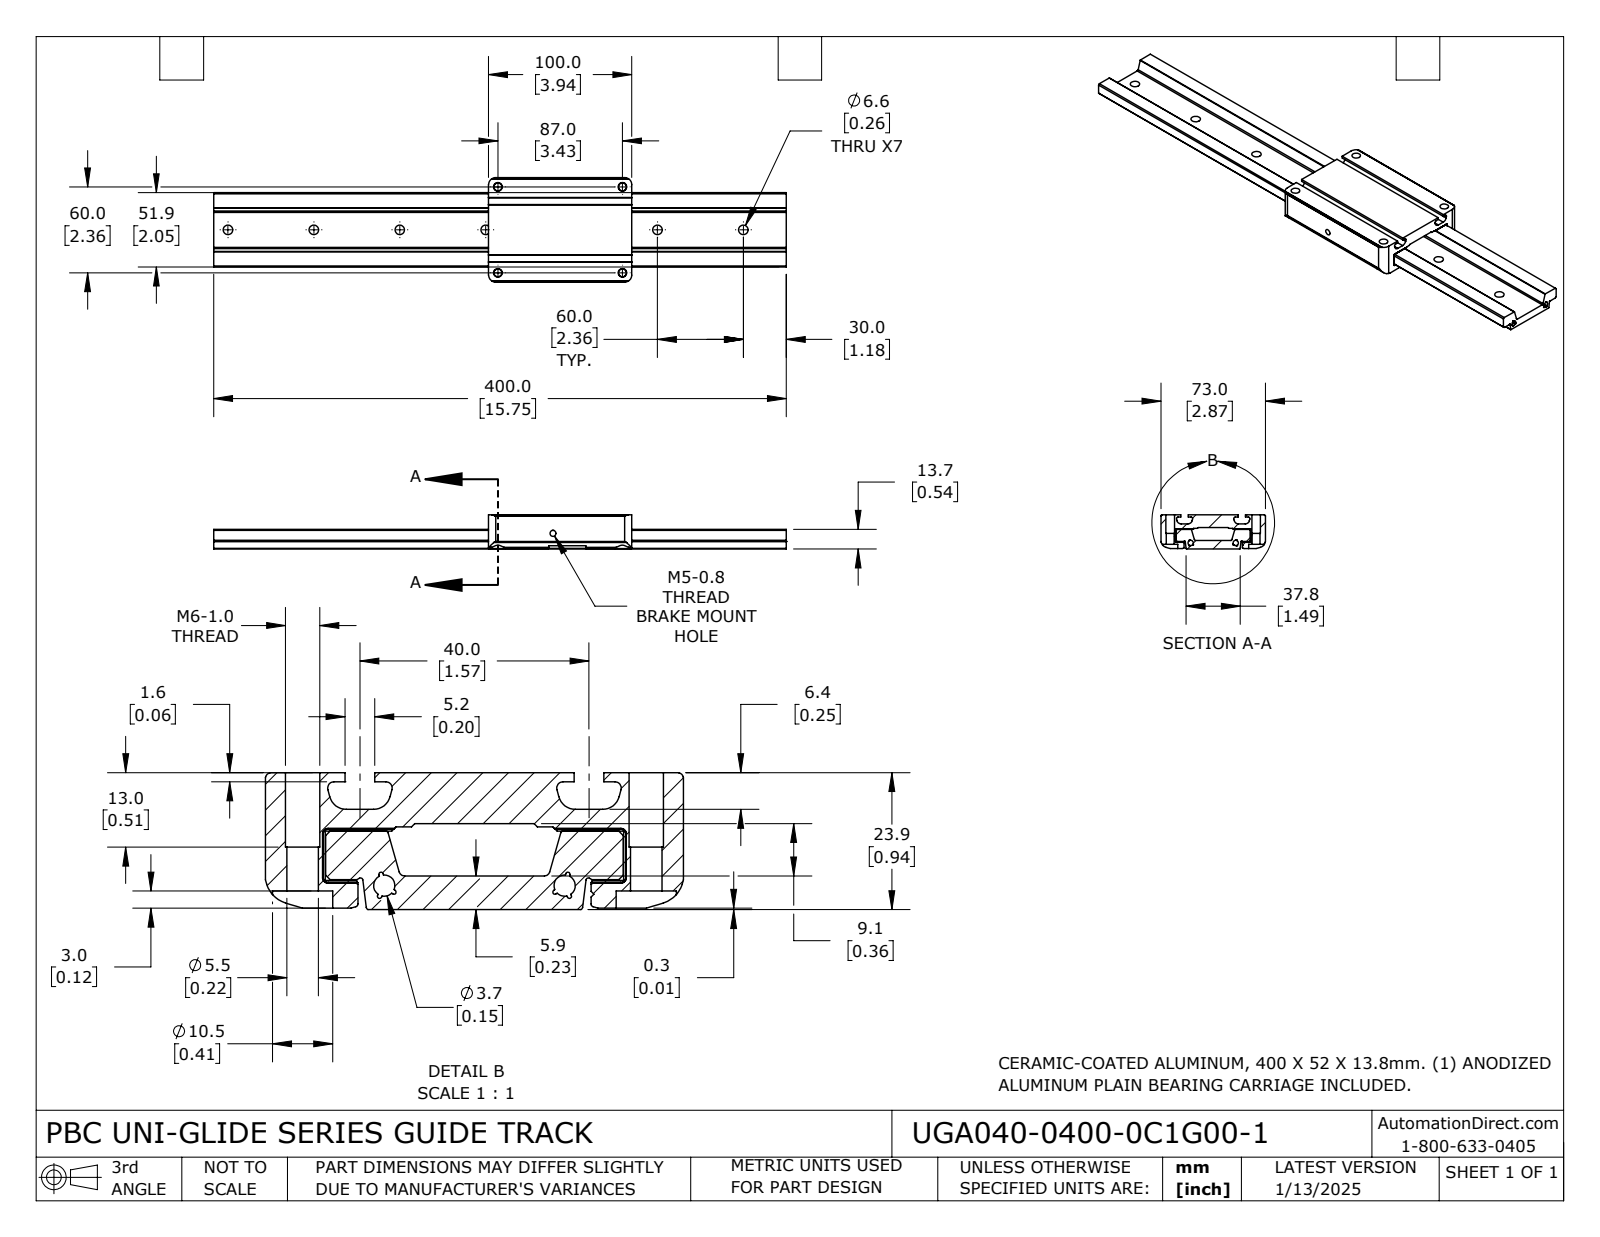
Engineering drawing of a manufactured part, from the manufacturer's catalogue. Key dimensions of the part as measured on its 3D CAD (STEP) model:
Part name (STEP PRODUCT): UGA040-0400-0C1G00-1_CARRIAGE; UGA040-0400-0C1G00-1; UGA040-0400-0C1G00-1_RAIL
STEP written by: SolidWorks 2023 (CONFIG_CONTROL_DESIGN)
Units: inches
Bodies: 10 solids, 396 faces (214 planar, 163 cylindrical, 19 other)
Overall size (bounding box): 15.748 × 2.874 × 0.941
Volume: 14.66 in³ · Surface area: 176.5 in²
Round holes (diameter × count): ⌀0.261 ×7, ⌀0.098 ×4, ⌀0.118 ×4, ⌀0.217 ×4, ⌀0.236 ×4, ⌀0.413 ×4, ⌀0.146 ×2, ⌀0.165 ×1
Partial cylindrical surfaces — rounded edges, fillets, slot ends (radius × count): R0.039 ×8, R0.094 ×8, R0.015 ×6, R0.02 ×6, R0.197 ×6, R0.035 ×4, R0.043 ×4, R0.118 ×4
Main face-to-face distances: 0.231, 0.539, 0.308, 0.941, 0.71, 0.402, 0.019, 0.015, 0.333, 0.207
Hole centre spacings: 2.362, 4.724, 7.087, 9.449, 0.591, 1.156, 1.214, 1.221
